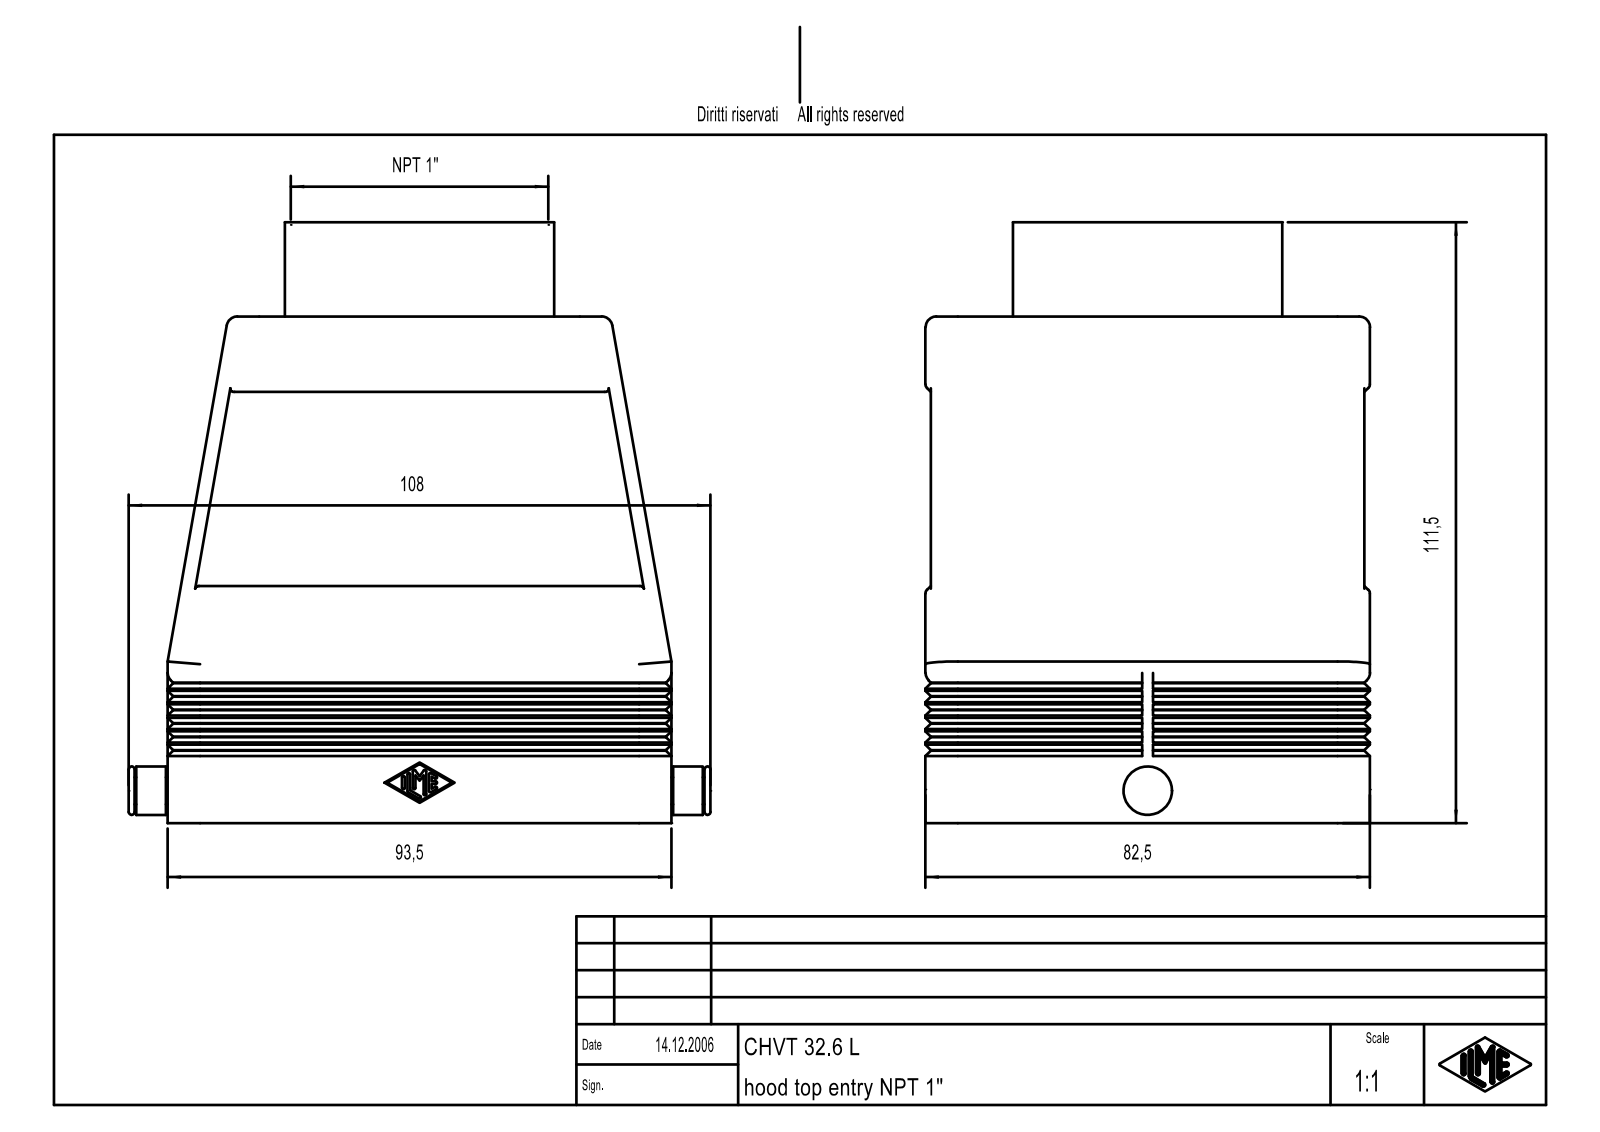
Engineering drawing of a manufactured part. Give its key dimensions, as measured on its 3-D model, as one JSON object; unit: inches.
{"part_name": "CHV_32_L; CHV_32_L.stp", "step_written_by": "Creo Elements/Direct Modeling 18.0B 02-Dec-2011 (C) Parametric Technology GmbH (AUTOMOTIVE_DESIGN)", "units": "inches", "bodies": {"solids": 1, "faces": 478, "planar": 244, "cylindrical": 146, "other": 88}, "overall_size": [4.39, 4.252, 3.248], "volume_in3": 11.52, "surface_area_in2": 123.3, "round_holes": [[0.097, 8], [0.138, 8]], "round_bosses_or_shafts": [[2.362, 1], [1.969, 1], [0.354, 1], [0.197, 1]], "partial_cylinders_radius": [[0.079, 16], [0.01, 14], [0.236, 8], [0.039, 4], [0.118, 4], [0.197, 4]], "face_to_face_distances": [0.157, 2.933, 3.091, 0.039, 0.118, 3.209, 3.051, 3.248, 0.07, 3.169], "hole_center_spacings": [1.063, 1.358, 3.051, 3.231, 3.34, 0.295, 2.421, 3.065]}
